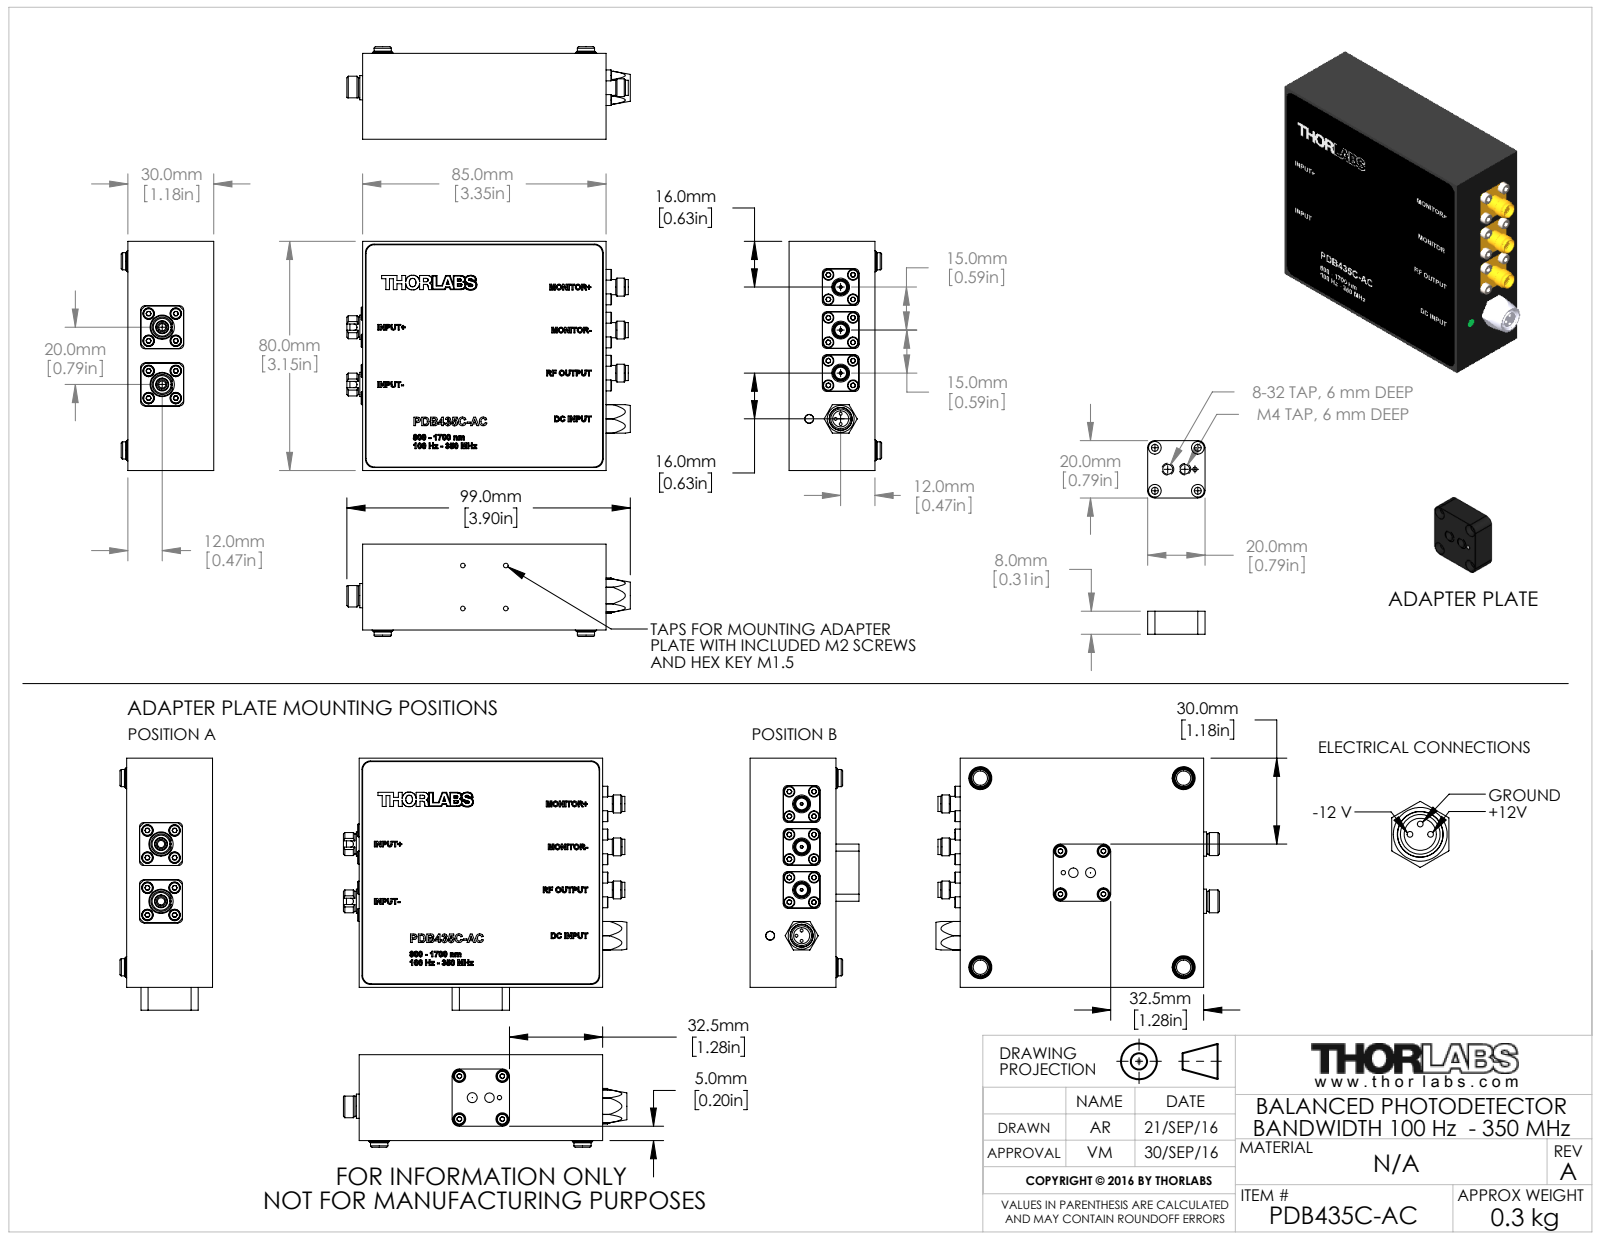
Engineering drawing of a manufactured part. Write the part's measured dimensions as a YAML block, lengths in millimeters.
part_name: "MTN005475-E0W"
step_written_by: "SolidWorks 2014 (AUTOMOTIVE_DESIGN)"
units: millimeters
bodies: {solids: 90, faces: 3108, planar: 1791, cylindrical: 584, other: 733}
overall_size: [99, 88, 38]
volume: 87719
surface_area: 57809
round_holes:
  - {diameter: 1.6, count: 38}
  - {diameter: 2.6, count: 12}
  - {diameter: 2.2, count: 8}
  - {diameter: 2.4, count: 8}
  - {diameter: 4, count: 8}
  - {diameter: 4.4, count: 8}
  - {diameter: 1.02, count: 6}
  - {diameter: 8, count: 5}
  - {diameter: 0.8, count: 3}
  - {diameter: 1, count: 3}
  - {diameter: 4.1, count: 3}
  - {diameter: 4.2, count: 3}
round_bosses_or_shafts:
  - {diameter: 3.8, count: 20}
  - {diameter: 2, count: 20}
  - {diameter: 4.5, count: 8}
  - {diameter: 2.5, count: 8}
  - {diameter: 0.43, count: 6}
  - {diameter: 6, count: 4}
  - {diameter: 6.22, count: 3}
  - {diameter: 5.3, count: 3}
partial_cylinders:
  - {radius: 1.5, count: 20}
  - {radius: 3, count: 12}
  - {radius: 2.5, count: 8}
  - {radius: 5, count: 8}
  - {radius: 1, count: 4}
  - {radius: 9.5, count: 2}
  - {radius: 5.75, count: 1}
face_to_face_distances: [29.7, 6, 23.7, 5.5, 80, 2, 74.5, 85, 3.5, 83]
hole_center_spacings: [15, 6.08, 8.6, 9.5, 6.72, 8.75, 11.53, 12.9]
